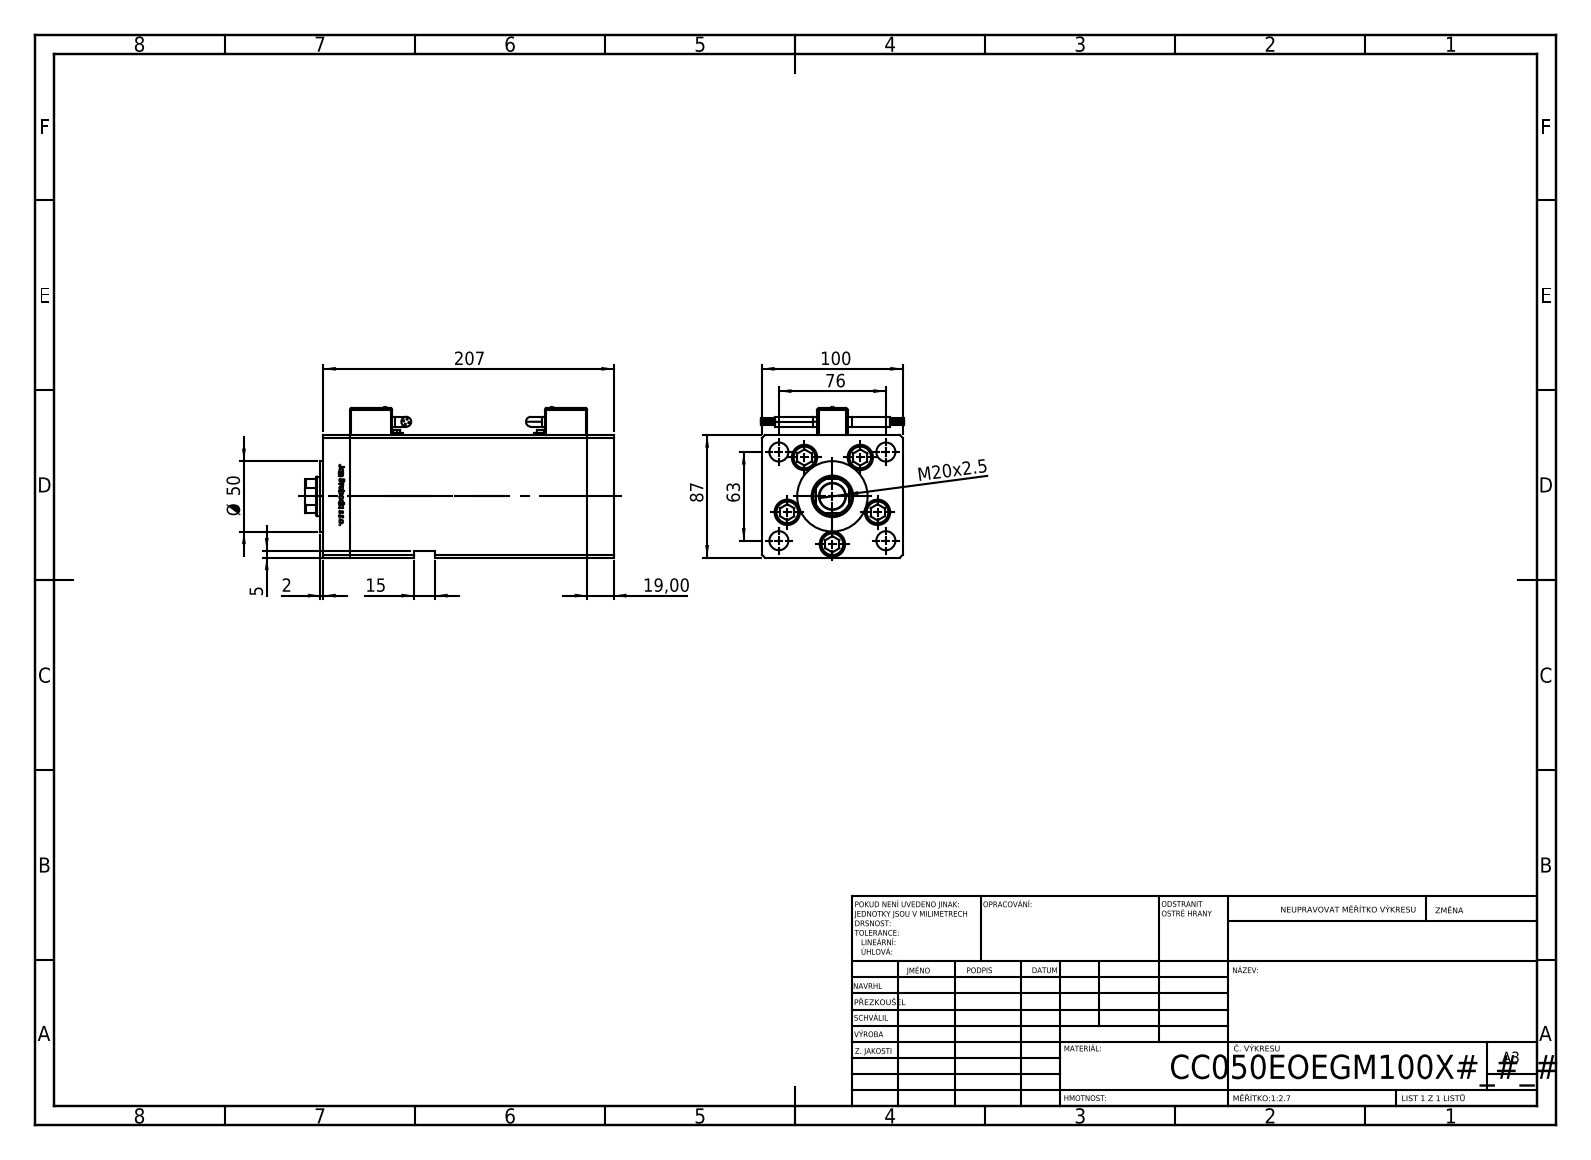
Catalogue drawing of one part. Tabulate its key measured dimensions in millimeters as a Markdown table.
| quantity | value |
| --- | --- |
| part name | V220C_VC_E; Magnetic_Switch_MSU4; V220C BACK_E; V220C_E MIDDLE (+2 more) |
| STEP written by | SolidWorks 2019 (CONFIG_CONTROL_DESIGN) |
| units | millimeters |
| bodies | 16 solids, 1419 faces (553 planar, 256 cylindrical, 610 other) |
| overall size | 219.5 × 107.1 × 101.6 |
| volume | 1 546 000 mm³ |
| surface area | 244 752 mm² |
| round holes (diameter × count) | 13.5 × 11, 18 × 5, 18.5 × 5, 12.5 × 4, 2 × 2, 3.6 × 2, 5 × 2, 7 × 2, 13.16 × 2, 28 × 1, 29.5 × 1 |
| round bosses / shafts (diameter × count) | 0.85 × 8, 17 × 5, 8 × 5, 7 × 4, 6 × 2, 3.5 × 2, 2.5 × 2, 50 × 1 |
| partial cylindrical surfaces (radius × count) | 1 × 24, 4 × 4, 0.93 × 2, 13.5 × 1 |
| main face-to-face distances | 100, 87, 19, 168.5, 187.5, 34.25, 206.5, 15.25, 153.25, 172.25 |
| hole center spacings | 34, 18.59, 39.64, 49.36, 57.95, 8.25, 21.03, 38.08 |
